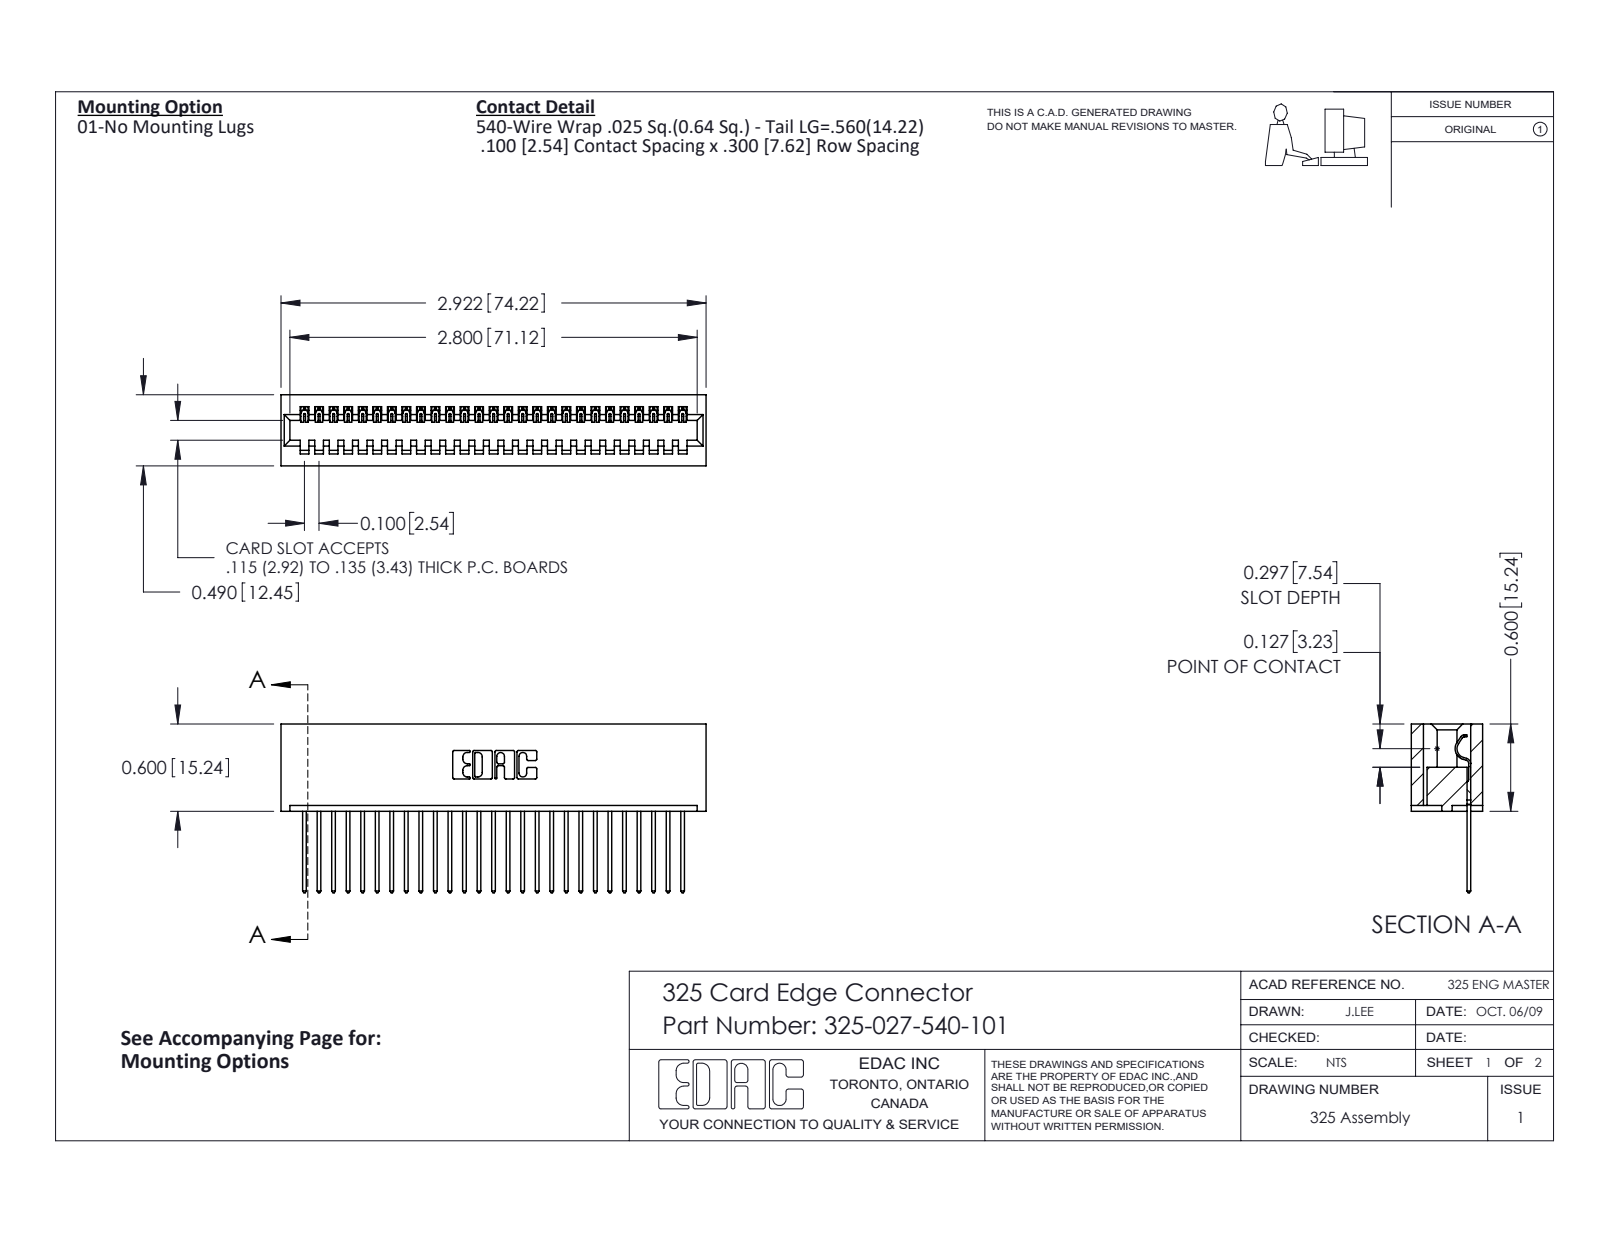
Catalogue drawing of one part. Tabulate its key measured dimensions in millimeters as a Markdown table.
| quantity | value |
| --- | --- |
| part name | 325 Part_Lugless; 325-292-001_325-293-140; 325-027-540-101 |
| STEP written by | SolidWorks 2016 (CONFIG_CONTROL_DESIGN) |
| units | millimeters |
| bodies | 28 solids, 1672 faces (1200 planar, 472 cylindrical, 0 other) |
| overall size | 74.2 × 29.5 × 12.4 |
| volume | 9 910 mm³ |
| surface area | 11 340 mm² |
| partial cylindrical surfaces (radius × count) | 0.2 × 54, 0.3 × 54, 0.3 × 22, 0.2 × 6, 0.8 × 6, 0.7 × 3, 0.4 × 1, 0.6 × 1 |
| main face-to-face distances | 2.1, 10.3, 7.6, 12.4, 2.7, 9.7, 0.6, 8.3, 2.5, 5.1 |
